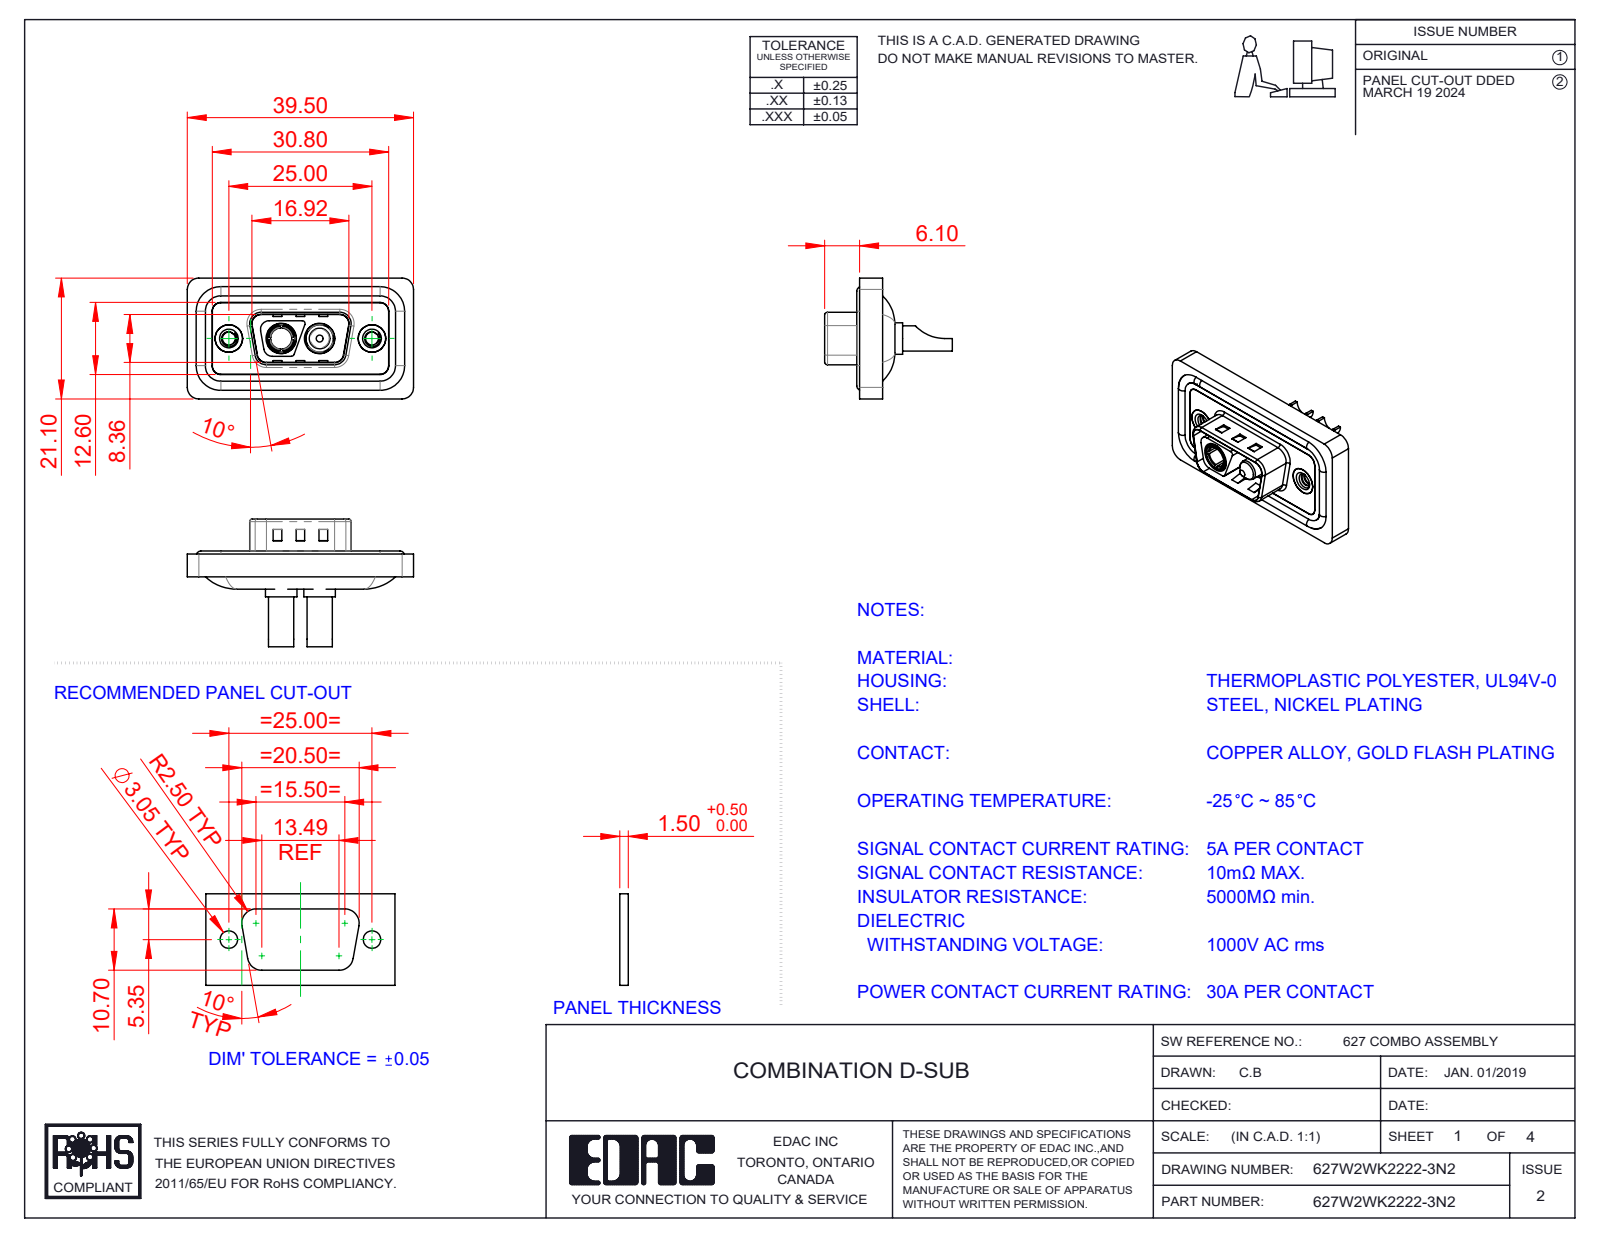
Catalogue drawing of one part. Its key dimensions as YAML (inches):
part_name: "627Combo Housing_2WK2; 627Combo Threaded Rivet_2; 627Combo Waterproof Housing_09 Contacts; Power Pin_30A SC (+4 more)"
step_written_by: "SolidWorks 2023 (CONFIG_CONTROL_DESIGN)"
units: inches
bodies: {solids: 11, faces: 546, planar: 195, cylindrical: 233, other: 118}
overall_size: [1.555, 0.878, 0.831]
volume: 0.281
surface_area: 11.71
round_holes:
  - {diameter: 0.089, count: 2}
  - {diameter: 0.138, count: 2}
  - {diameter: 0.157, count: 2}
  - {diameter: 0.189, count: 2}
  - {diameter: 0.191, count: 2}
  - {diameter: 0.197, count: 2}
  - {diameter: 0.209, count: 2}
  - {diameter: 0.146, count: 1}
round_bosses_or_shafts:
  - {diameter: 0.063, count: 4}
  - {diameter: 0.217, count: 2}
  - {diameter: 0.205, count: 2}
  - {diameter: 0.193, count: 2}
  - {diameter: 0.187, count: 2}
  - {diameter: 0.173, count: 2}
  - {diameter: 0.148, count: 2}
  - {diameter: 0.195, count: 1}
partial_cylinders:
  - {radius: 0.059, count: 24}
  - {radius: 0.079, count: 18}
  - {radius: 0.02, count: 10}
  - {radius: 0.063, count: 8}
  - {radius: 0.01, count: 4}
  - {radius: 0.024, count: 4}
  - {radius: 0.026, count: 4}
  - {radius: 0.035, count: 4}
face_to_face_distances: [0.016, 0.043, 0.114, 0.02, 0.122, 0.063, 0.059, 0.098, 0.071, 0.126]
hole_center_spacings: [0.36, 0.624, 0.265, 0.984]
